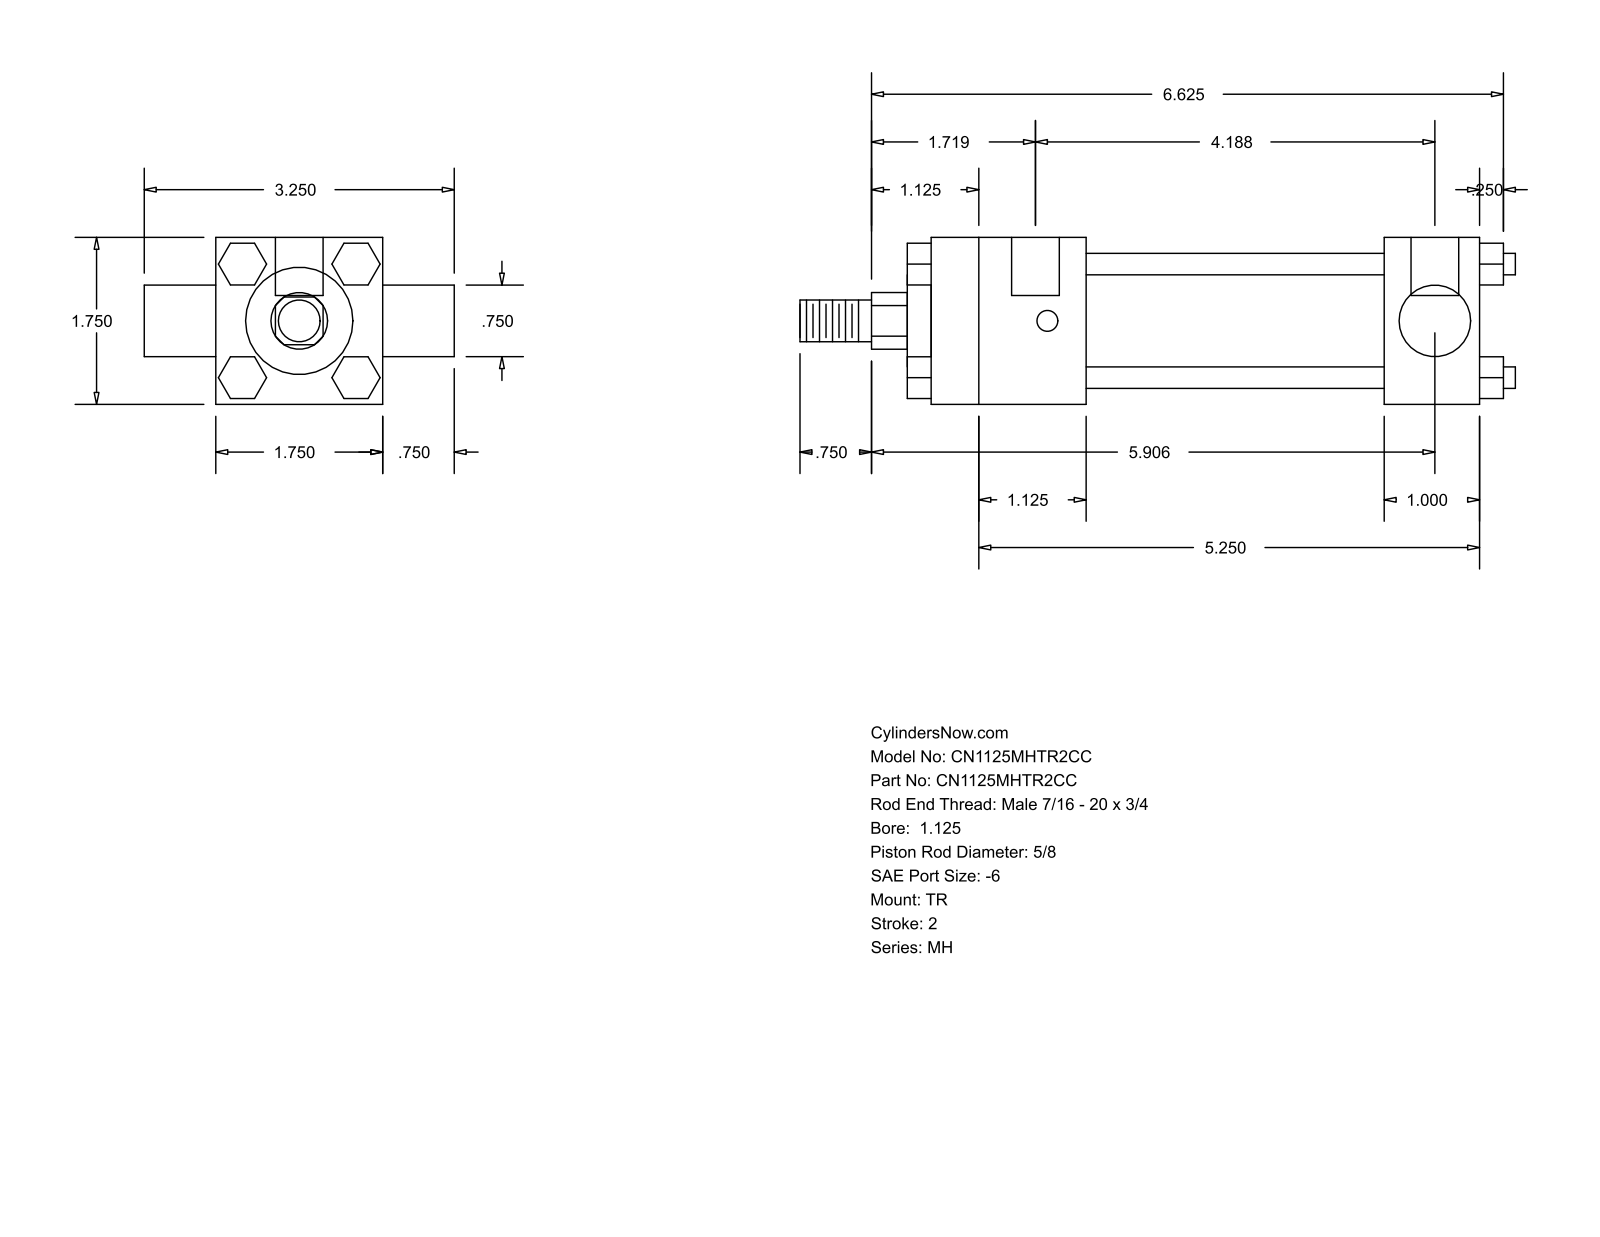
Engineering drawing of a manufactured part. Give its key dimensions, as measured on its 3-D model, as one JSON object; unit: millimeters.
{"part_name": "MH_TR__0112_0.625", "step_written_by": "GSSL Pune (CONFIG_CONTROL_DESIGN)", "units": "millimeters", "bodies": {"solids": 0, "faces": 120, "planar": 92, "cylindrical": 28, "other": 0}, "overall_size": [190.5, 82.55, 44.45], "round_holes": [[5.56, 3], [12.7, 2]], "round_bosses_or_shafts": [[5.71, 4], [34.92, 1], [28.57, 1], [19.05, 1], [15.88, 1], [11.11, 1]], "partial_cylinders_radius": [[7.54, 1]], "face_to_face_distances": [44.46, 6.35, 152.4, 11.11, 25.4, 79.38, 104.78, 41.27, 120.65, 146.05], "hole_center_spacings": [3.17, 103.19, 106.36]}
